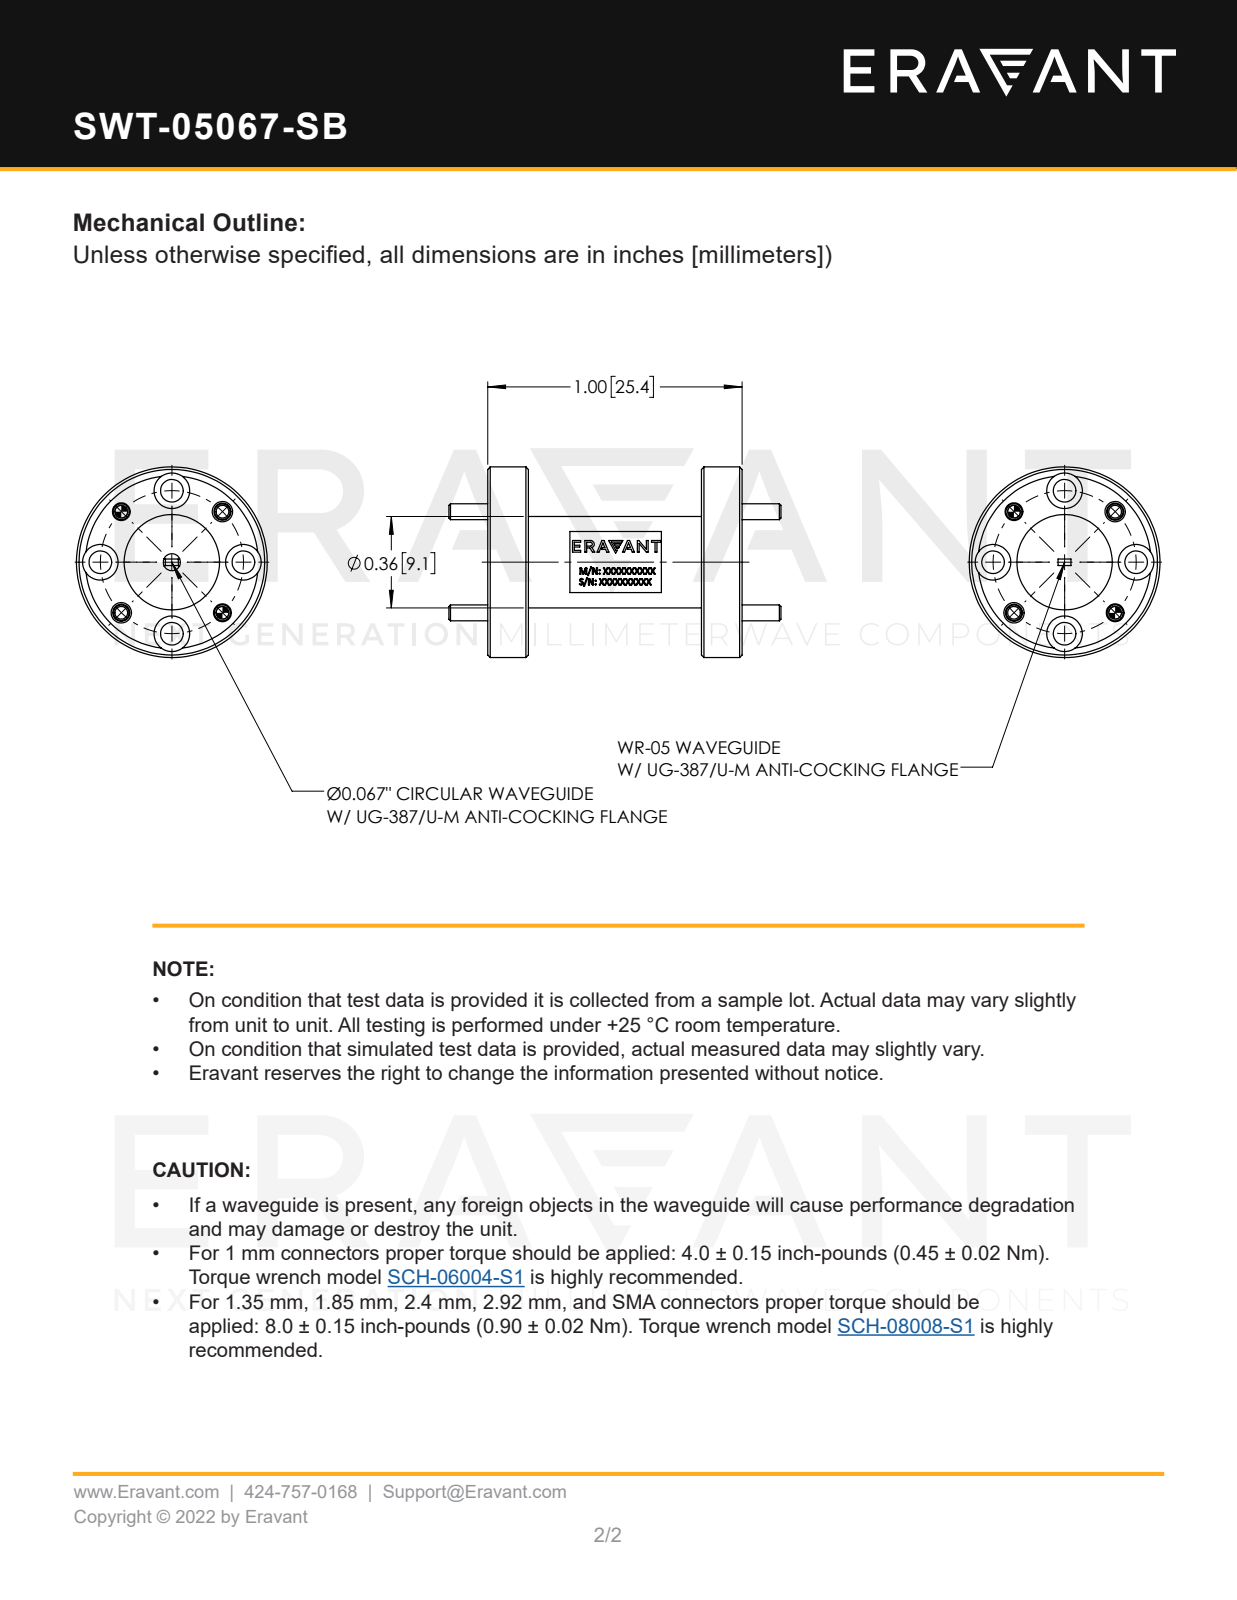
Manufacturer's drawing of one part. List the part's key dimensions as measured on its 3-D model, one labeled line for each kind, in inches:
Part name (STEP PRODUCT): SWT-05067-SB
STEP written by: SolidWorks 2021 (CONFIG_CONTROL_DESIGN)
Units: inches
Bodies: 5 solids, 148 faces (26 planar, 74 cylindrical, 48 other)
Overall size (bounding box): 1.305 × 0.75 × 0.75
Volume: 0.19 in³ · Surface area: 3.866 in²
Round holes (diameter × count): ⌀0.061 ×4, ⌀0.067 ×4, ⌀0.089 ×4, ⌀0.14 ×4, ⌀0.68 ×1
Round bosses / shafts (diameter × count): ⌀0.063 ×4, ⌀0.75 ×1, ⌀0.375 ×1, ⌀0.375 ×1, ⌀0.36 ×1
Main face-to-face distances: 0.98, 0.02, 0.68, 0.82, 0.14, 0.14, 0.82, 0.96, 0.84, 0.16
Hole centre spacings: 0.215, 0.398, 0.281, 0.519, 0.562, 0.52, 0.281, 0.563
